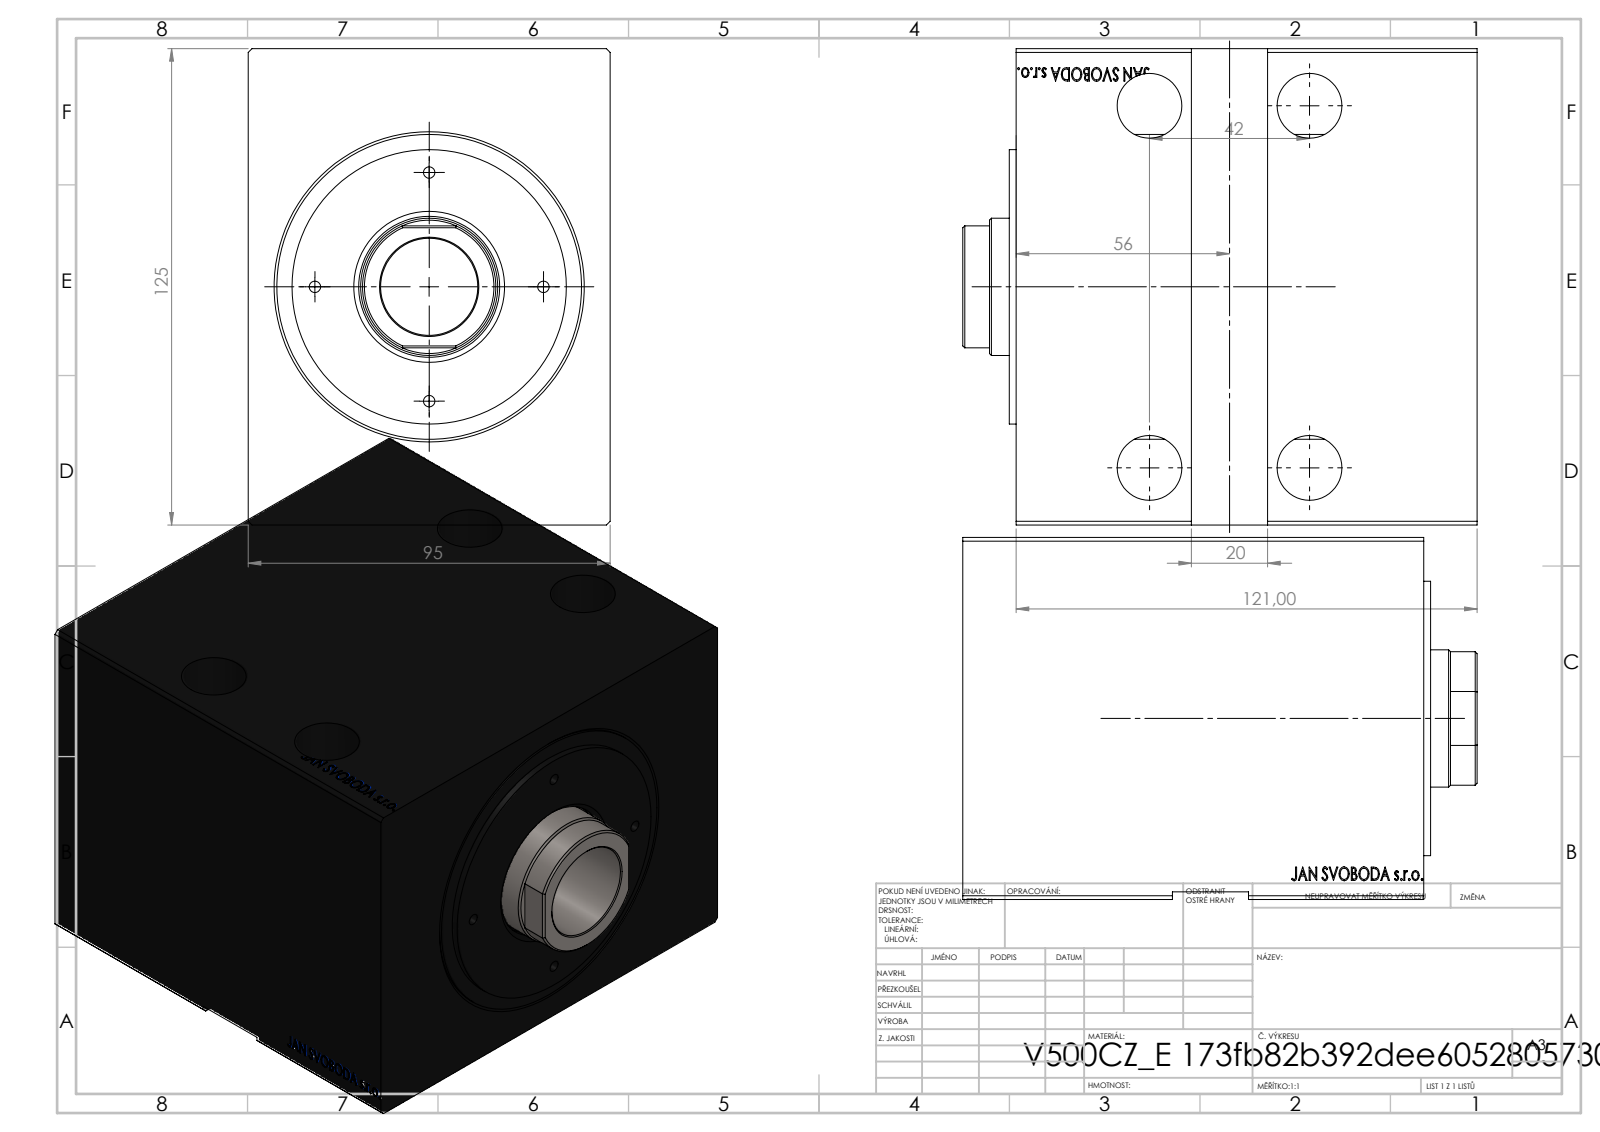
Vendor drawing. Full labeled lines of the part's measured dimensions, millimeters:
STEP written by: SolidWorks 2019 (CONFIG_CONTROL_DESIGN)
Units: millimetres
Bodies: 1 solid, 777 faces (381 planar, 14 cylindrical, 382 other)
Overall size (bounding box): 125 × 121 × 95
Volume: 852 077 mm³ · Surface area: 119 918 mm²
Round holes (diameter × count): ⌀17 ×4, ⌀36 ×1, ⌀63 ×1, ⌀80 ×1
Main face-to-face distances: 95, 125, 121, 102.5, 18.5, 2, 93, 91, 11.5, 30
Hole centre spacings: 42, 95, 103.87
